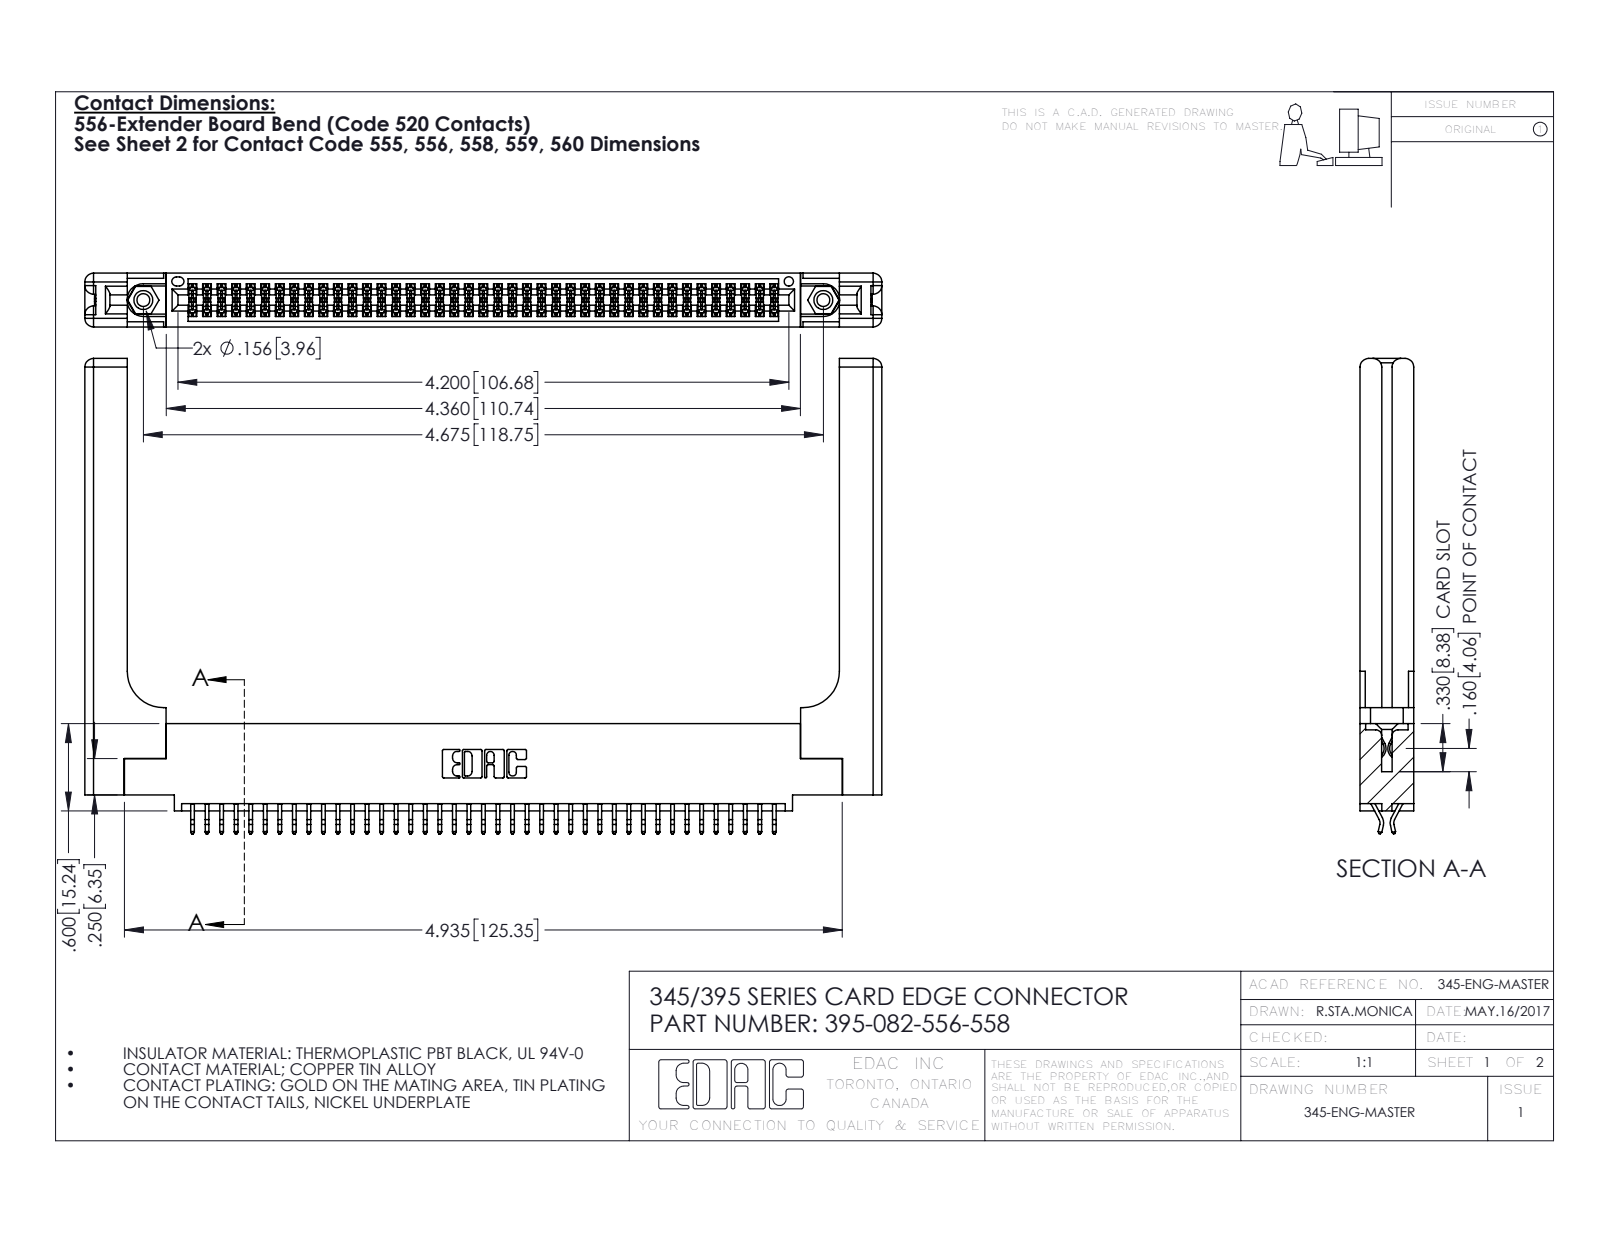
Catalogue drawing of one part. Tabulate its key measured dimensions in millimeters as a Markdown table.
| quantity | value |
| --- | --- |
| part name | 395-082-556-558; 345 Part_0.110 Offset - 0.156 Dia-TH; 345-292-001_556 Tail; 345-220-058_345-220-058 (+1 more) |
| STEP written by | SolidWorks 2016 (CONFIG_CONTROL_DESIGN) |
| units | millimeters |
| bodies | 87 solids, 4978 faces (3266 planar, 1652 cylindrical, 60 other) |
| overall size | 139.2 × 83 × 9.4 |
| volume | 21 910 mm³ |
| surface area | 24 920 mm² |
| round holes (diameter × count) | 2.3 × 2, 3.2 × 2, 4 × 2, 1.6 × 1 |
| round bosses / shafts (diameter × count) | 3.9 × 2 |
| partial cylindrical surfaces (radius × count) | 0.2 × 123, 0.3 × 22, 1.5 × 16, 0.2 × 6, 0.8 × 6, 0.7 × 3, 0.3 × 2, 0.4 × 2 |
| main face-to-face distances | 1.8, 9.4, 7.6, 0.6, 5.1, 2.5, 6.9, 5.7, 3.8, 3.8 |
| hole center spacings | 6.9, 112.8, 118.7 |
